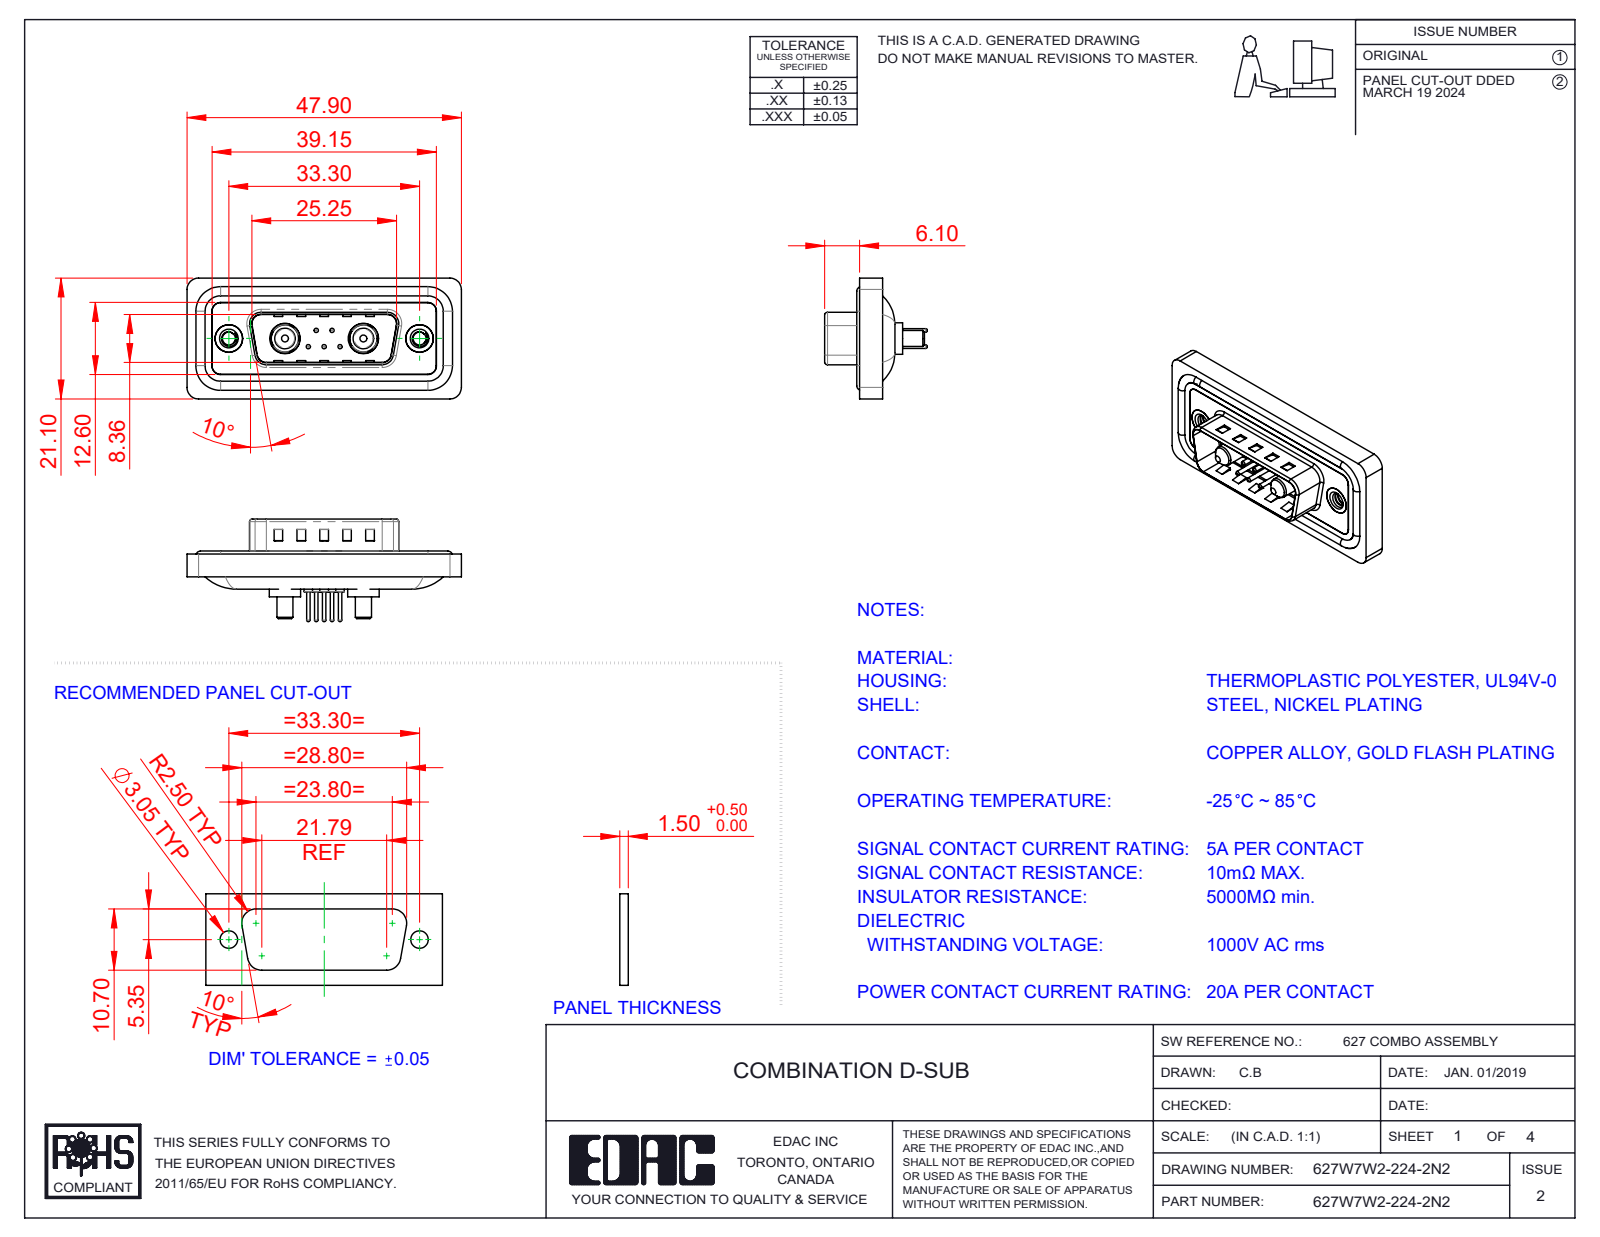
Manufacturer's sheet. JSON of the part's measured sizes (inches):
{"part_name": "627Combo Waterproof Housing_15 Contacts; 627Combo Shell Front_15 Contacts; 627Combo Contact Row 1_24; 627Combo Contact Row 2_24 (+5 more)", "step_written_by": "SolidWorks 2023 (CONFIG_CONTROL_DESIGN)", "units": "inches", "bodies": {"solids": 16, "faces": 710, "planar": 232, "cylindrical": 292, "other": 186}, "overall_size": [1.886, 0.831, 0.705], "volume_in3": 0.337, "surface_area_in2": 13.63, "round_holes": [[0.03, 5], [0.063, 5], [0.079, 5], [0.089, 2], [0.157, 2], [0.189, 2], [0.191, 2], [0.197, 2], [0.209, 2]], "round_bosses_or_shafts": [[0.059, 5], [0.024, 5], [0.063, 4], [0.217, 2], [0.205, 2], [0.193, 2], [0.187, 2], [0.148, 2]], "partial_cylinders_radius": [[0.059, 26], [0.079, 20], [0.02, 8], [0.063, 8], [0.01, 4], [0.024, 4], [0.026, 4], [0.035, 4]], "face_to_face_distances": [0.016, 0.043, 0.059, 0.063, 0.02, 0.122, 0.114, 0.032, 0.377, 0.157], "hole_center_spacings": [0.124, 0.109, 0.386, 0.925, 0.17, 0.17, 0.198, 0.198]}
